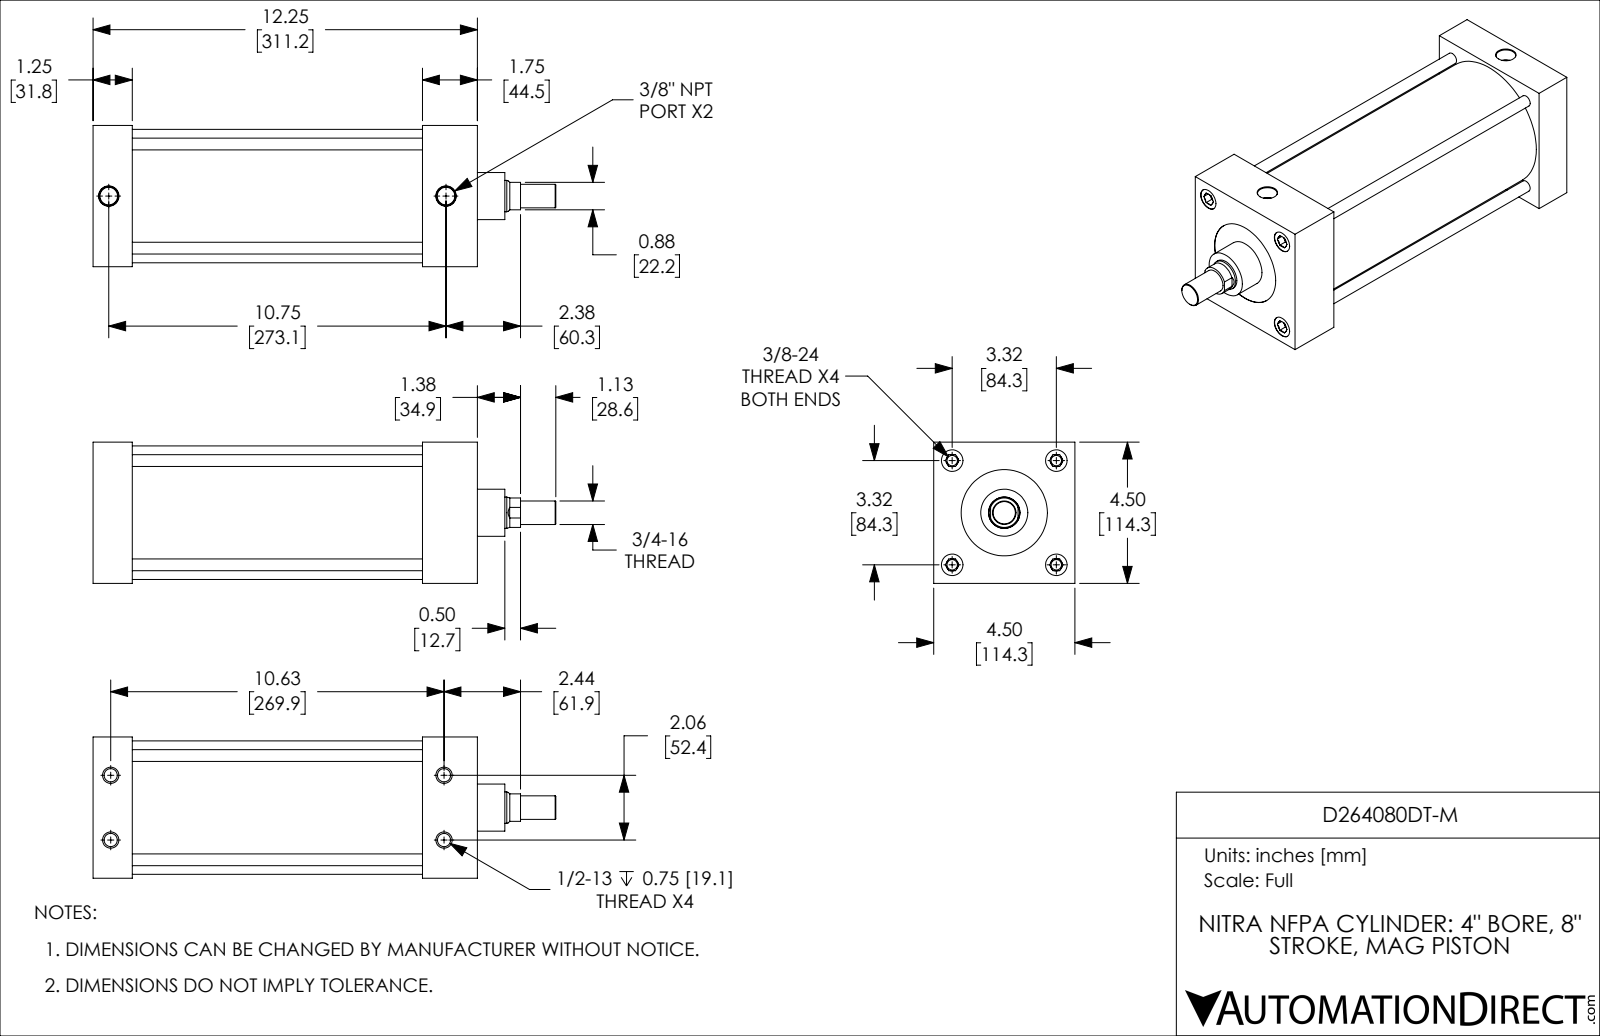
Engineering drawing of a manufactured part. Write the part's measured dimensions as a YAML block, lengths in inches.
part_name: "D264080DT-M_BODY; D264080DT-M_PISTON_KK1; D264080DT-M"
step_written_by: "SolidWorks 2019 (CONFIG_CONTROL_DESIGN)"
units: inches
bodies: {solids: 2, faces: 198, planar: 58, cylindrical: 62, other: 78}
overall_size: [14.75, 4.5, 4.5]
volume: 101.8
surface_area: 523.2
round_holes:
  - {diameter: 0.332, count: 4}
  - {diameter: 0.422, count: 4}
  - {diameter: 0.687, count: 4}
  - {diameter: 0.562, count: 2}
  - {diameter: 1.001, count: 1}
  - {diameter: 2.75, count: 1}
  - {diameter: 4.001, count: 1}
round_bosses_or_shafts:
  - {diameter: 0.375, count: 4}
  - {diameter: 4.251, count: 1}
  - {diameter: 3.999, count: 1}
  - {diameter: 1.5, count: 1}
  - {diameter: 0.999, count: 1}
  - {diameter: 0.75, count: 1}
partial_cylinders:
  - {radius: 0.469, count: 1}
face_to_face_distances: [1.25, 4.5, 10.5, 9.25, 12.25, 11, 1.75, 2.5, 8, 9.75]
hole_center_spacings: [2.347, 3.32, 10.737, 1.033, 4.695, 10.625, 10.823, 1.034]
